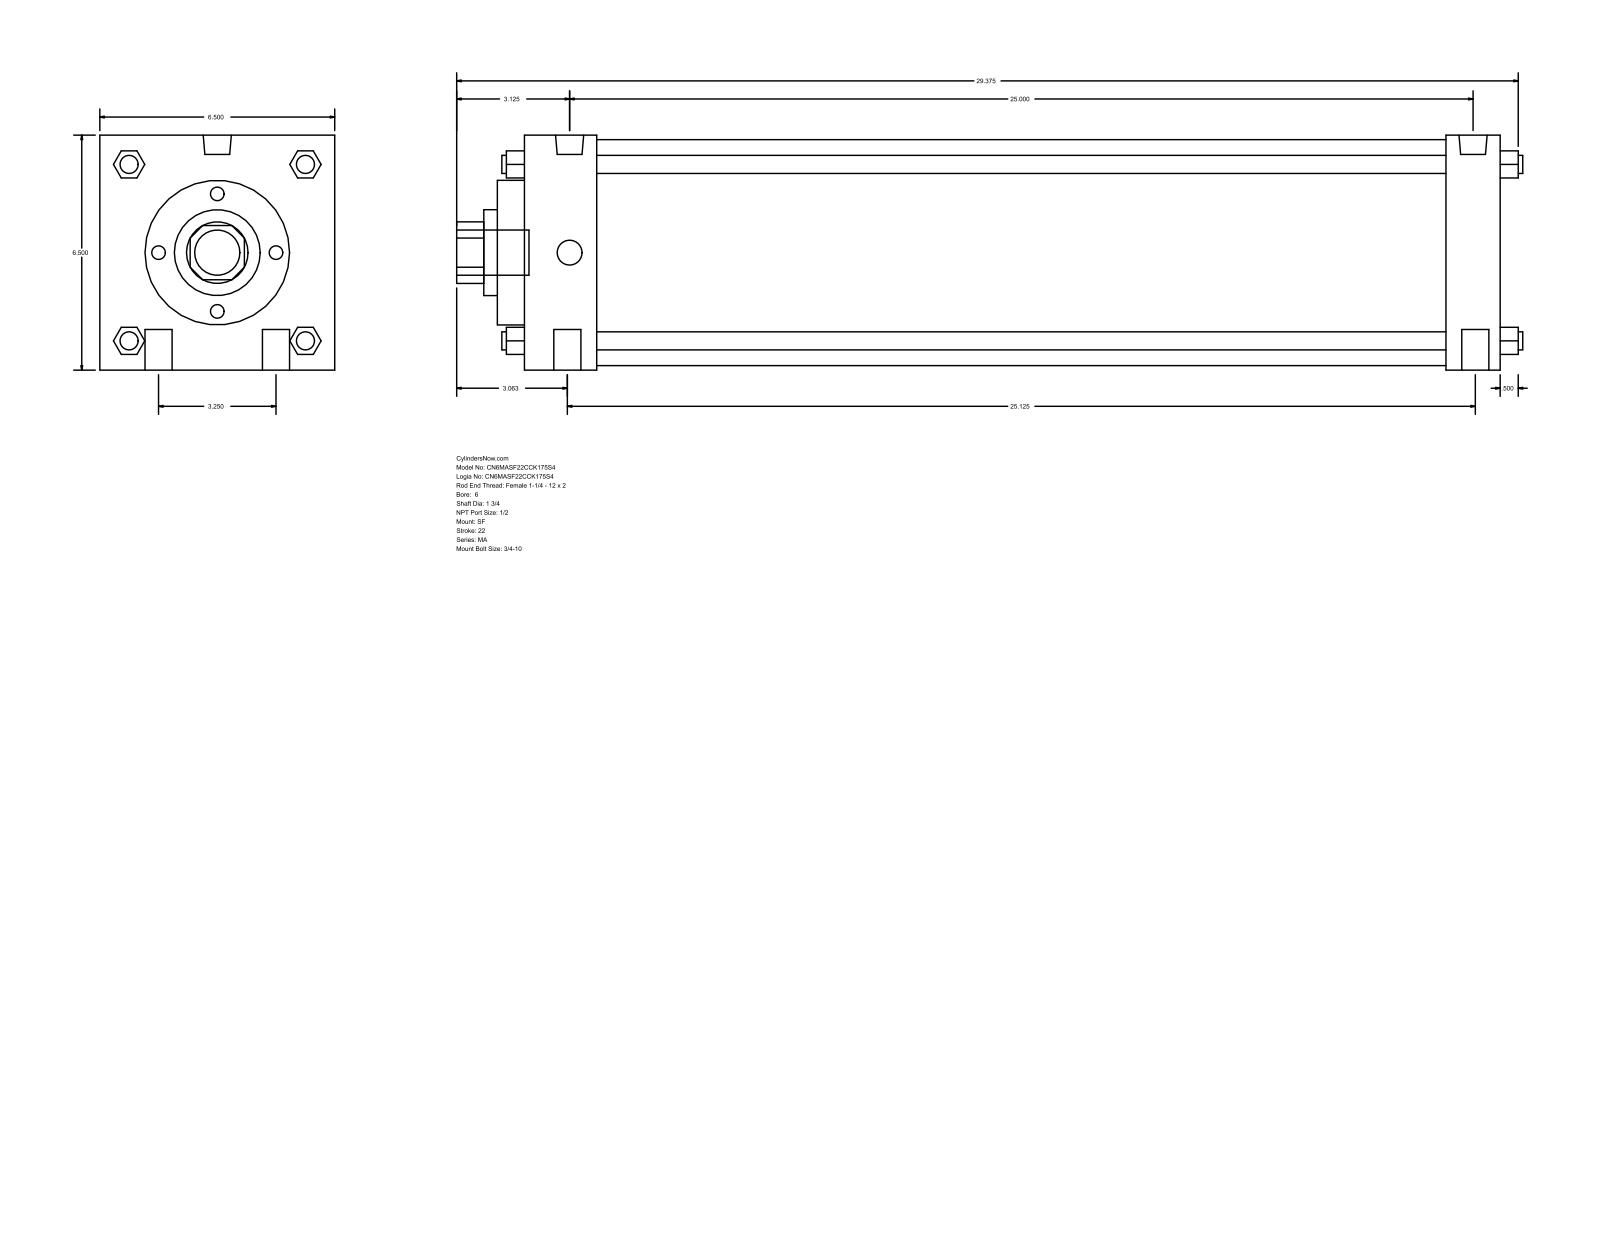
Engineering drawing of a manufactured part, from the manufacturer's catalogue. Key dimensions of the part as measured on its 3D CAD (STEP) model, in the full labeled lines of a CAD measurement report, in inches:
Part name (STEP PRODUCT): MA_SF__0600_1.75
STEP written by: GSSL Pune (CONFIG_CONTROL_DESIGN)
Units: inches
Bodies: 0 solids, 126 faces (95 planar, 31 cylindrical, 0 other)
Overall size (bounding box): 29.5 × 6.5 × 6.5
Round holes (diameter × count): ⌀1.75 ×1, ⌀2.375 ×1, ⌀4 ×1, ⌀6.25 ×1
Round bosses / shafts (diameter × count): ⌀0.75 ×4, ⌀0.5 ×4, ⌀0.778 ×2, ⌀0.687 ×2, ⌀1.25 ×1
Partial cylindrical surfaces — rounded edges, fillets, slot ends (radius × count): R0.852 ×1
Main face-to-face distances: 6.5, 27, 0.75, 2, 25.5, 1.5, 23.5, 25, 2.75, 26.25
